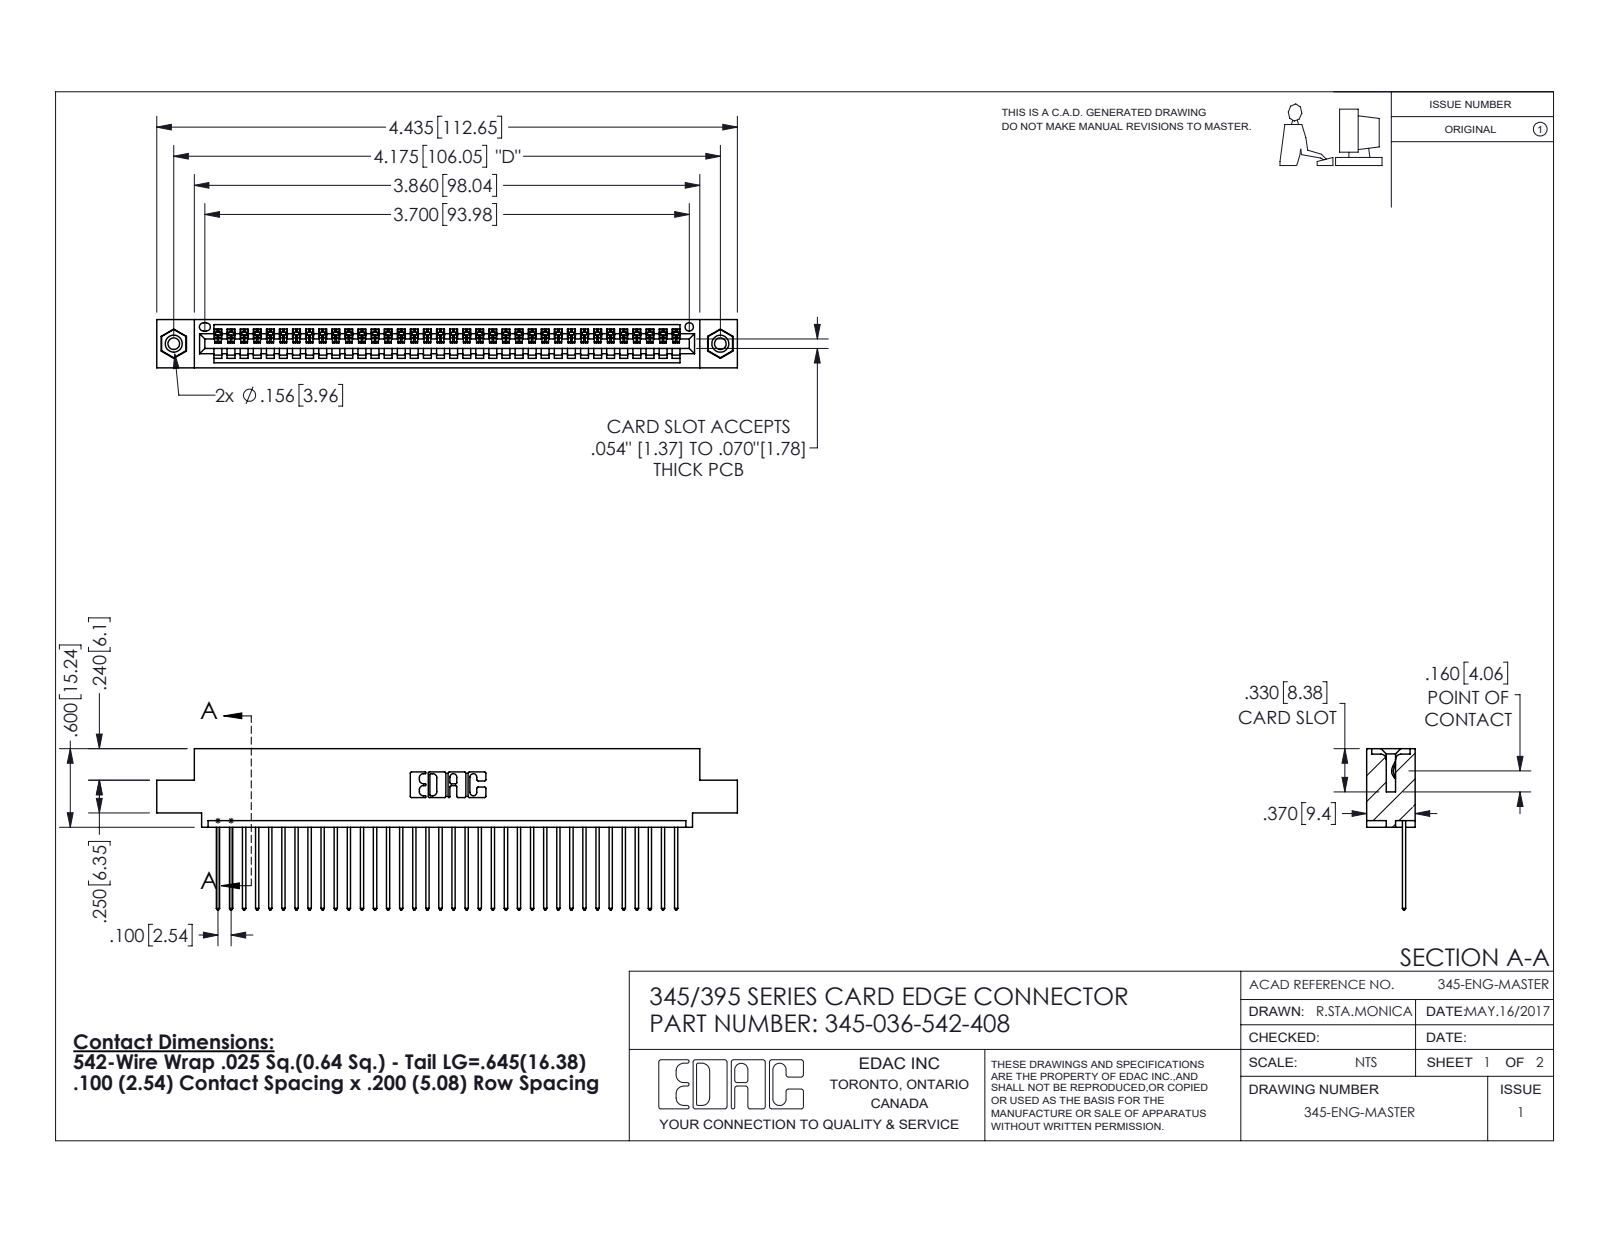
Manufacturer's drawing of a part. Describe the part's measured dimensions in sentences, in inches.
The part is named "345-250-001_345-250-003-102; 345-036-542-408; 345-292-001_345-293-142; 345 Part_0.110 Offset - 0.156 Dia-TI". Its 3-D file was written by "SolidWorks 2016 (CONFIG_CONTROL_DESIGN)". It is 39 solids with 2278 faces: 1556 planar, 706 cylindrical and 16 other. Overall it measures 4.435 by 1.232 by 0.37 inches. Its volume is 0.65 cubic inches and its surface area 22.75 square inches. Round holes: 2 of diameter 0.089, 2 of diameter 0.125, 2 of diameter 0.156, 1 of diameter 0.064. Round bosses or shafts: 2 of diameter 0.155. Partial cylindrical surfaces (rounded edges, fillets, slot ends): 72 of radius 0.006, 72 of radius 0.01, 22 of radius 0.01, 6 of radius 0.007, 6 of radius 0.031, 3 of radius 0.026, 2 of radius 0.031, 2 of radius 0.04. The main face-to-face distances are 0.072, 0.298, 0.37, 0.098, 0.272, 0.025, 0.2, 0.225, 0.149, 0.072. The hole center spacings are 0.27, 3.939, 4.175.
